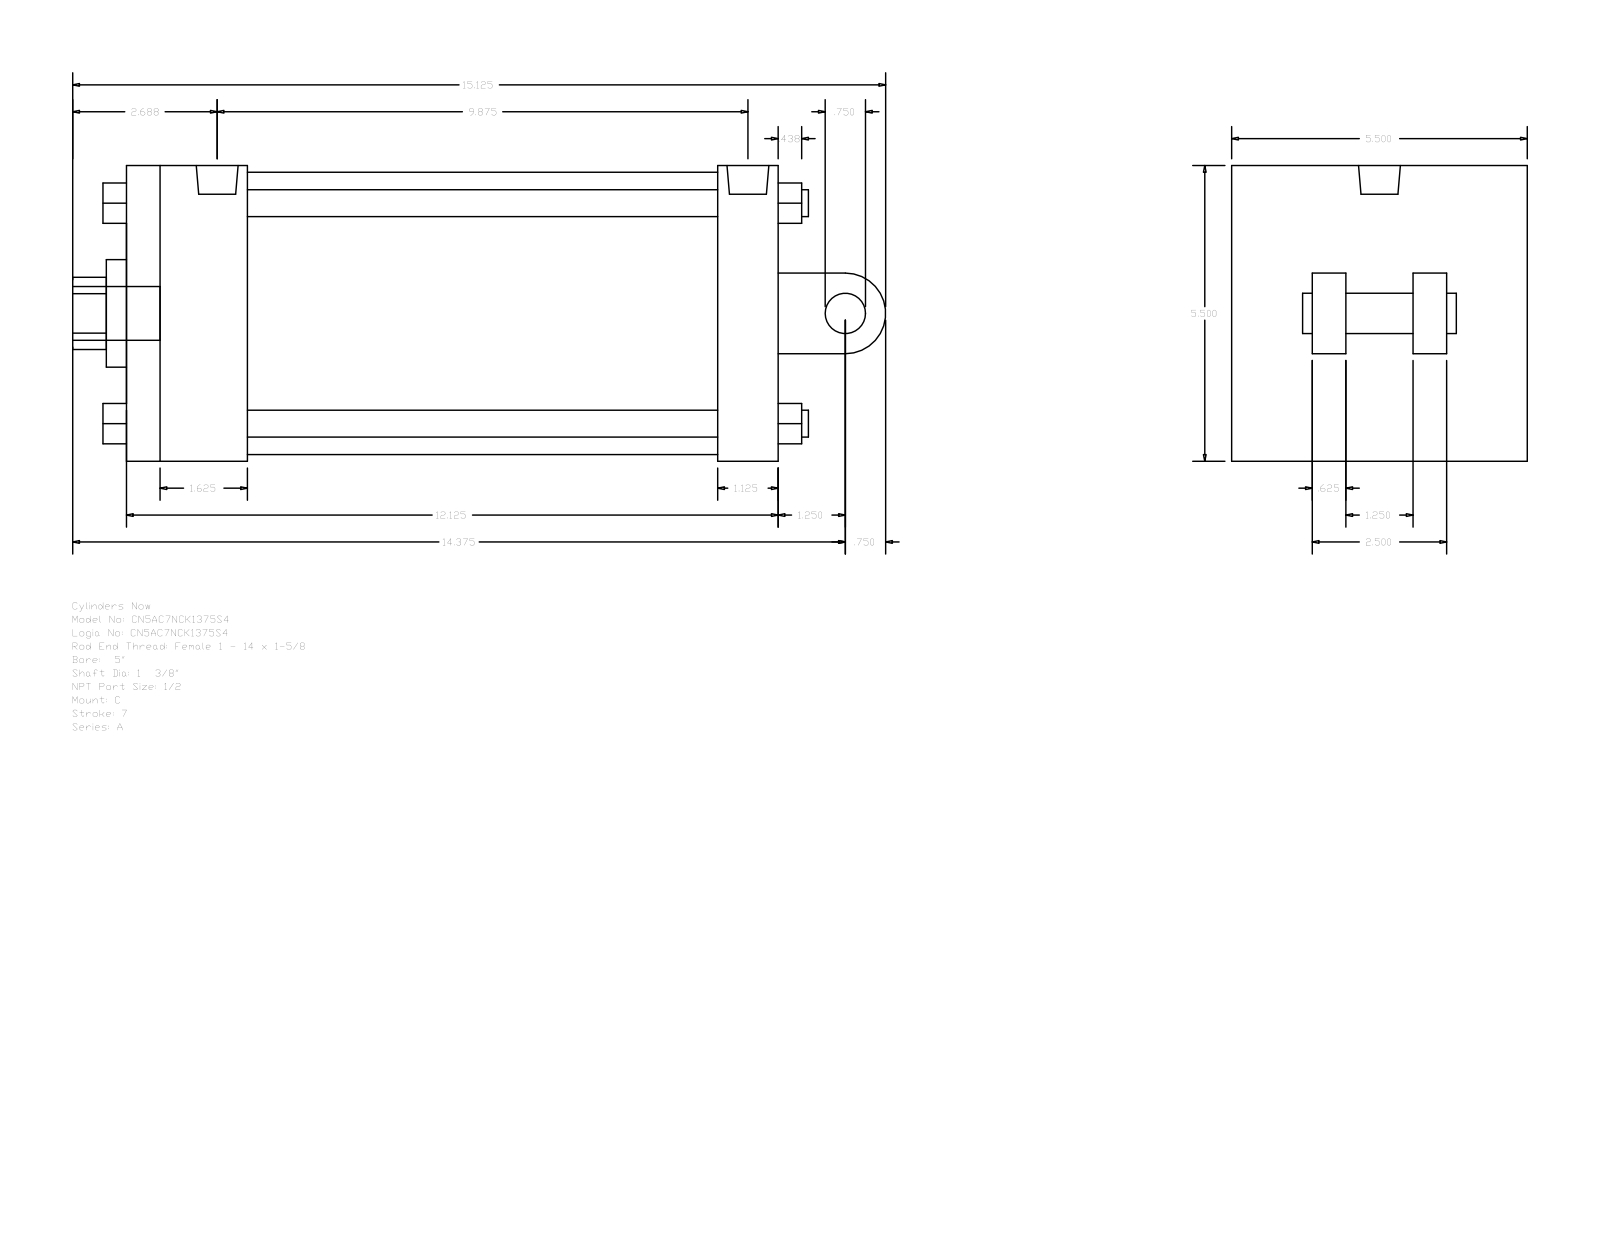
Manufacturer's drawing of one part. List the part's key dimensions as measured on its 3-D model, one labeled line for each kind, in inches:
Part name (STEP PRODUCT): A_C__0500_1.375
STEP written by: GSSL Pune (CONFIG_CONTROL_DESIGN)
Units: inches
Bodies: 0 solids, 135 faces (102 planar, 33 cylindrical, 0 other)
Overall size (bounding box): 15.125 × 5.5 × 5.5
Round holes (diameter × count): ⌀0.344 ×2, ⌀0.778 ×1, ⌀1.375 ×1, ⌀2 ×1, ⌀5.25 ×1
Round bosses / shafts (diameter × count): ⌀0.5 ×4, ⌀0.344 ×2, ⌀1 ×1, ⌀0.778 ×1, ⌀0.75 ×1
Partial cylindrical surfaces — rounded edges, fillets, slot ends (radius × count): R0.672 ×1, R0.75 ×1
Main face-to-face distances: 5.5, 12.125, 1.125, 2.25, 11, 8.75, 9.875, 1.5, 0.625, 4
Hole centre spacings: 0.094
